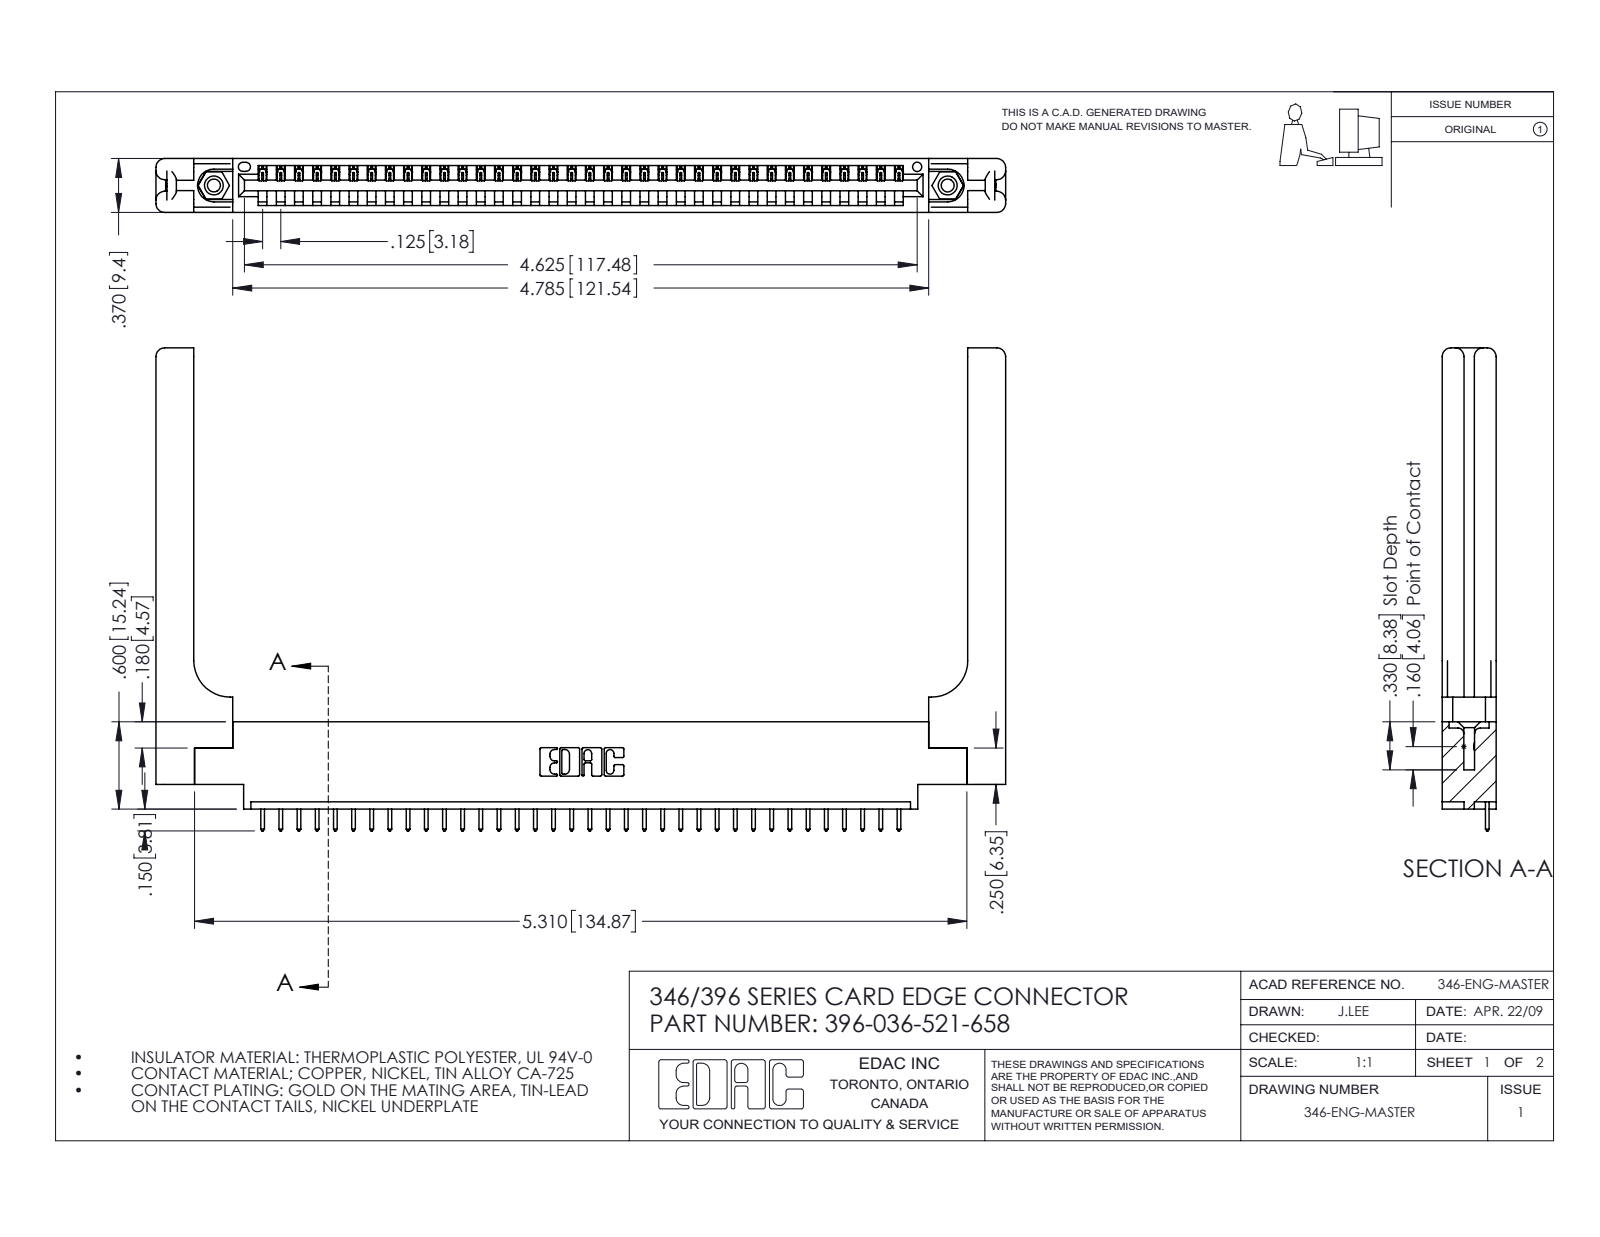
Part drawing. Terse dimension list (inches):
name: 346-220-058_345-220-058; 345-250-001_345-250-001-102; 346 Part_0.170 Offset - 0.156 Dia-TH; 396-036-521-658 (+1 more)
written by: SolidWorks 2016 (CONFIG_CONTROL_DESIGN)
unit: in
bodies: 41 solids, 2470 faces (1668 planar, 742 cylindrical, 60 other)
size: 5.841 × 3.32 × 0.37
volume: 1.307 in³; area: 34.46 in²
holes: 2× ⌀0.089, 2× ⌀0.125, 2× ⌀0.156, 1× ⌀0.064
bosses: 2× ⌀0.155
rounds: 72× R0.006, 72× R0.01, 22× R0.01, 16× R0.06, 6× R0.007, 6× R0.031, 3× R0.026, 2× R0.03
face distances: 0.37, 0.048, 0.322, 0.072, 0.148, 0.15, 0.25, 0.298, 0.025, 0.222
hole spacings: 0.246, 4.836, 5.045
